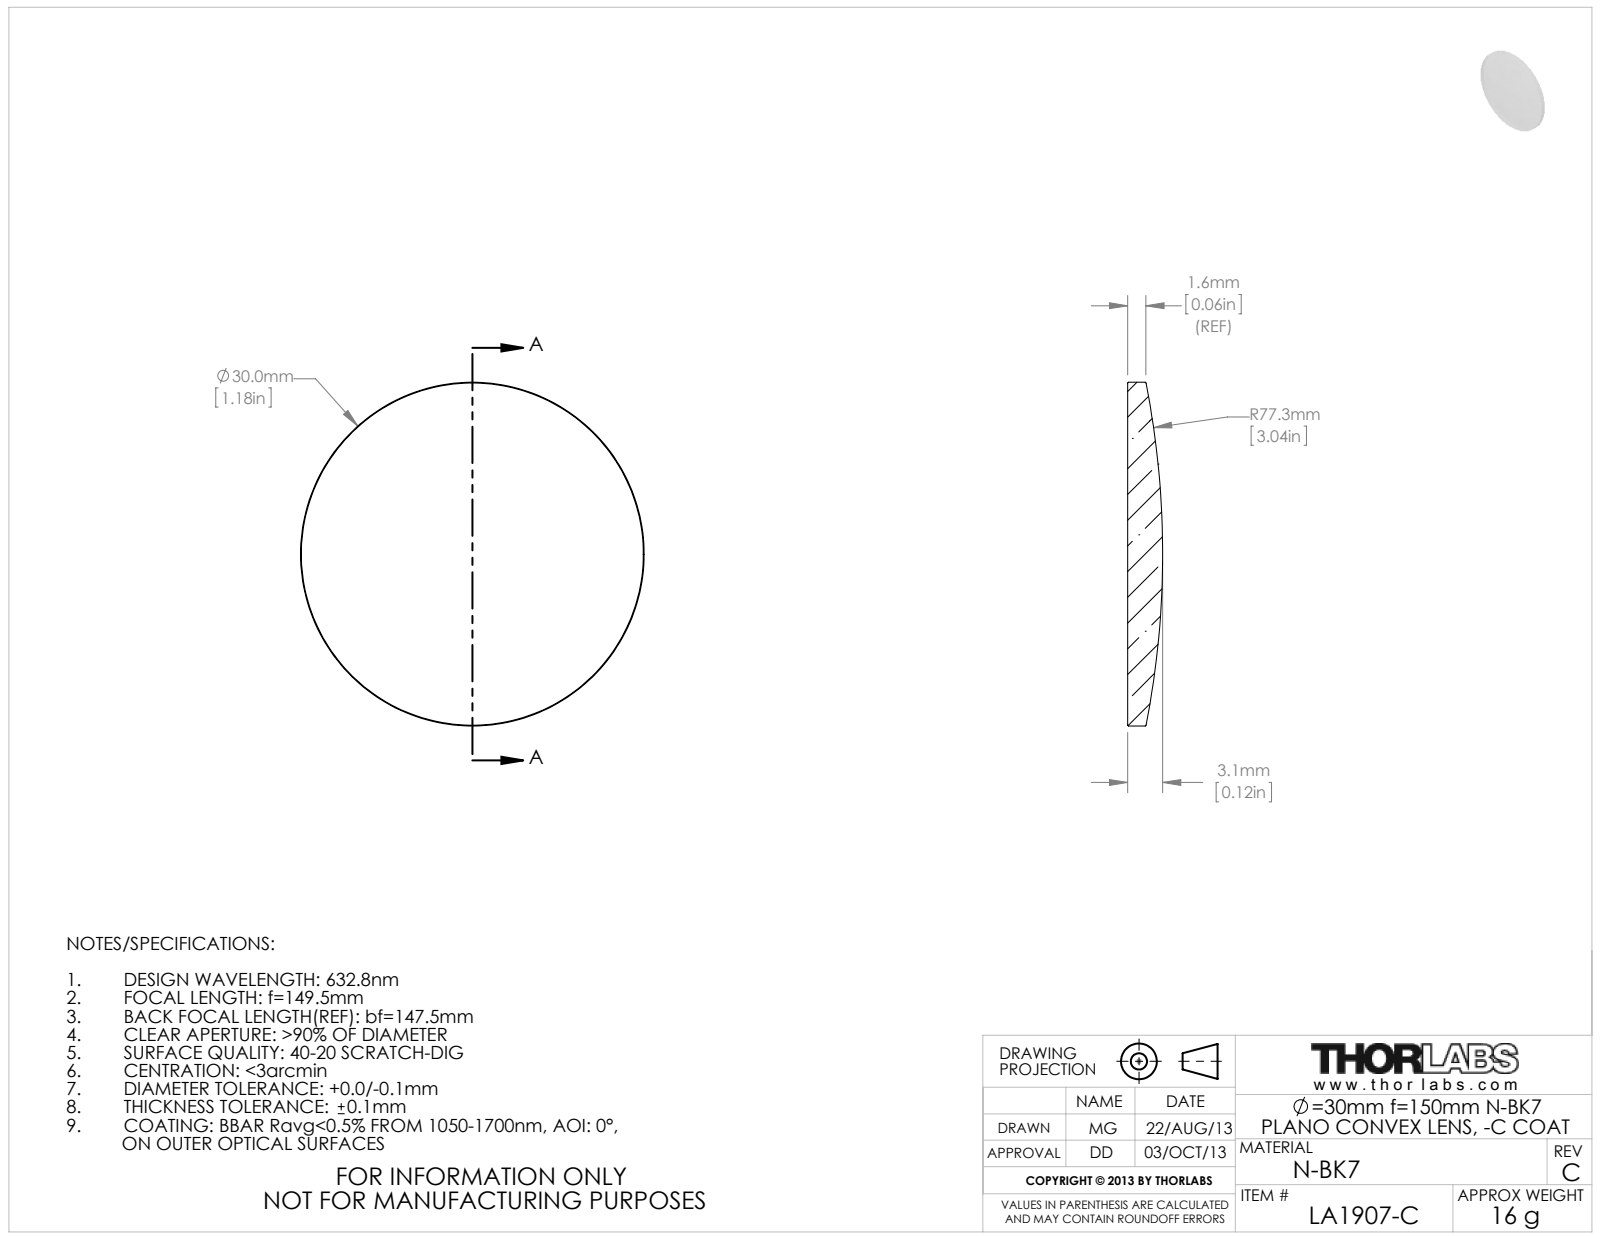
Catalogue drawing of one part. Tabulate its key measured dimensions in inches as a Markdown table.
| quantity | value |
| --- | --- |
| part name | 19308-E0W |
| STEP written by | SolidWorks 2009 (AUTOMOTIVE_DESIGN) |
| units | inches |
| bodies | 1 solid, 5 faces (1 planar, 2 cylindrical, 2 other) |
| overall size | 1.181 × 1.181 × 0.12 |
| volume | 0.1 in³ |
| surface area | 2.432 in² |
| round bosses / shafts (diameter × count) | 1.181 × 1 |
